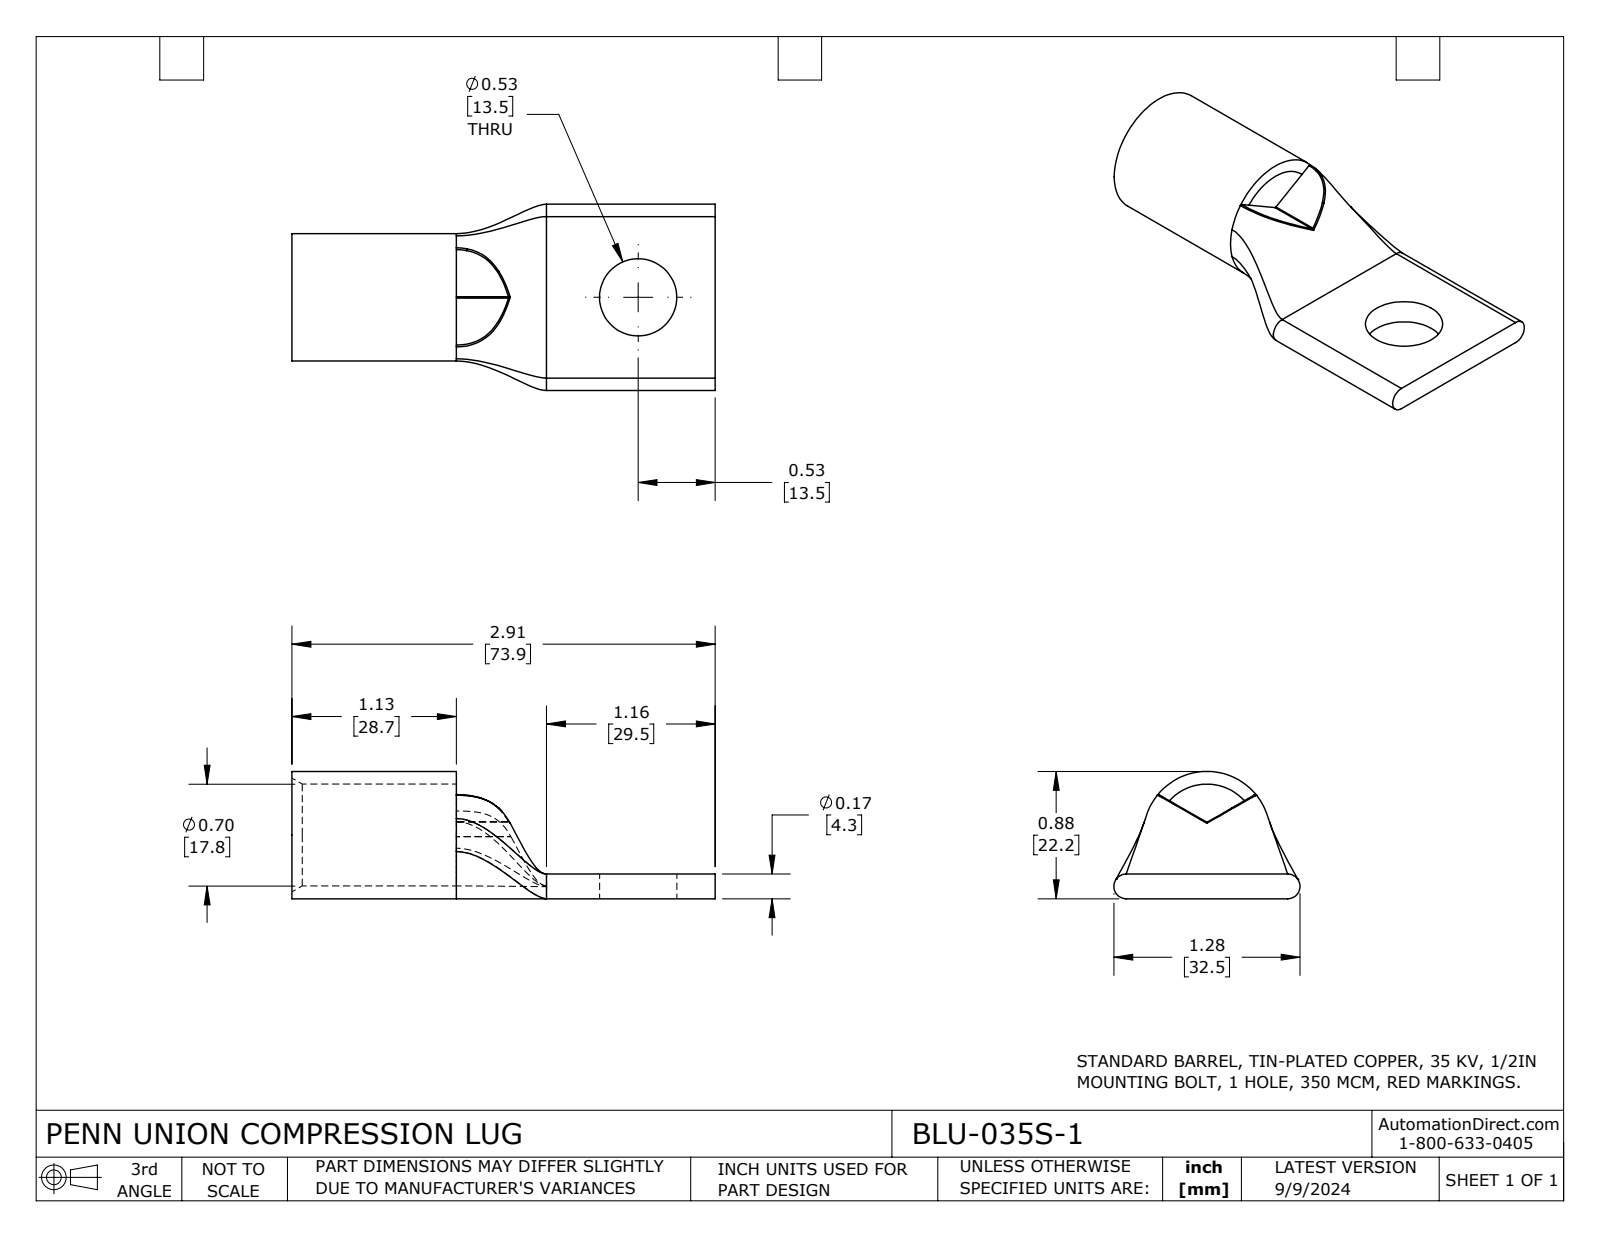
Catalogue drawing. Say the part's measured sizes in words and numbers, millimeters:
The part is named "BLU-035S-1". Its 3-D file was written by "SolidWorks 2023 (CONFIG_CONTROL_DESIGN)". It is 1 solid with 37 faces: 11 planar, 11 cylindrical and 15 other. Overall it measures 73.9 by 32.5 by 22.2 millimeters. Its volume is 9 370 cubic millimeters and its surface area 8 110 square millimeters. Round holes: 1 of diameter 13.5, 1 of diameter 17.8. Round bosses or shafts: 1 of diameter 22.2. Partial cylindrical surfaces (rounded edges, fillets, slot ends): 2 of radius 0.3, 2 of radius 2.2. The main face-to-face distances are 4.3, 2.2, 73.9, 28.7, 45.2, 44.5, 15.7, 29.5.
